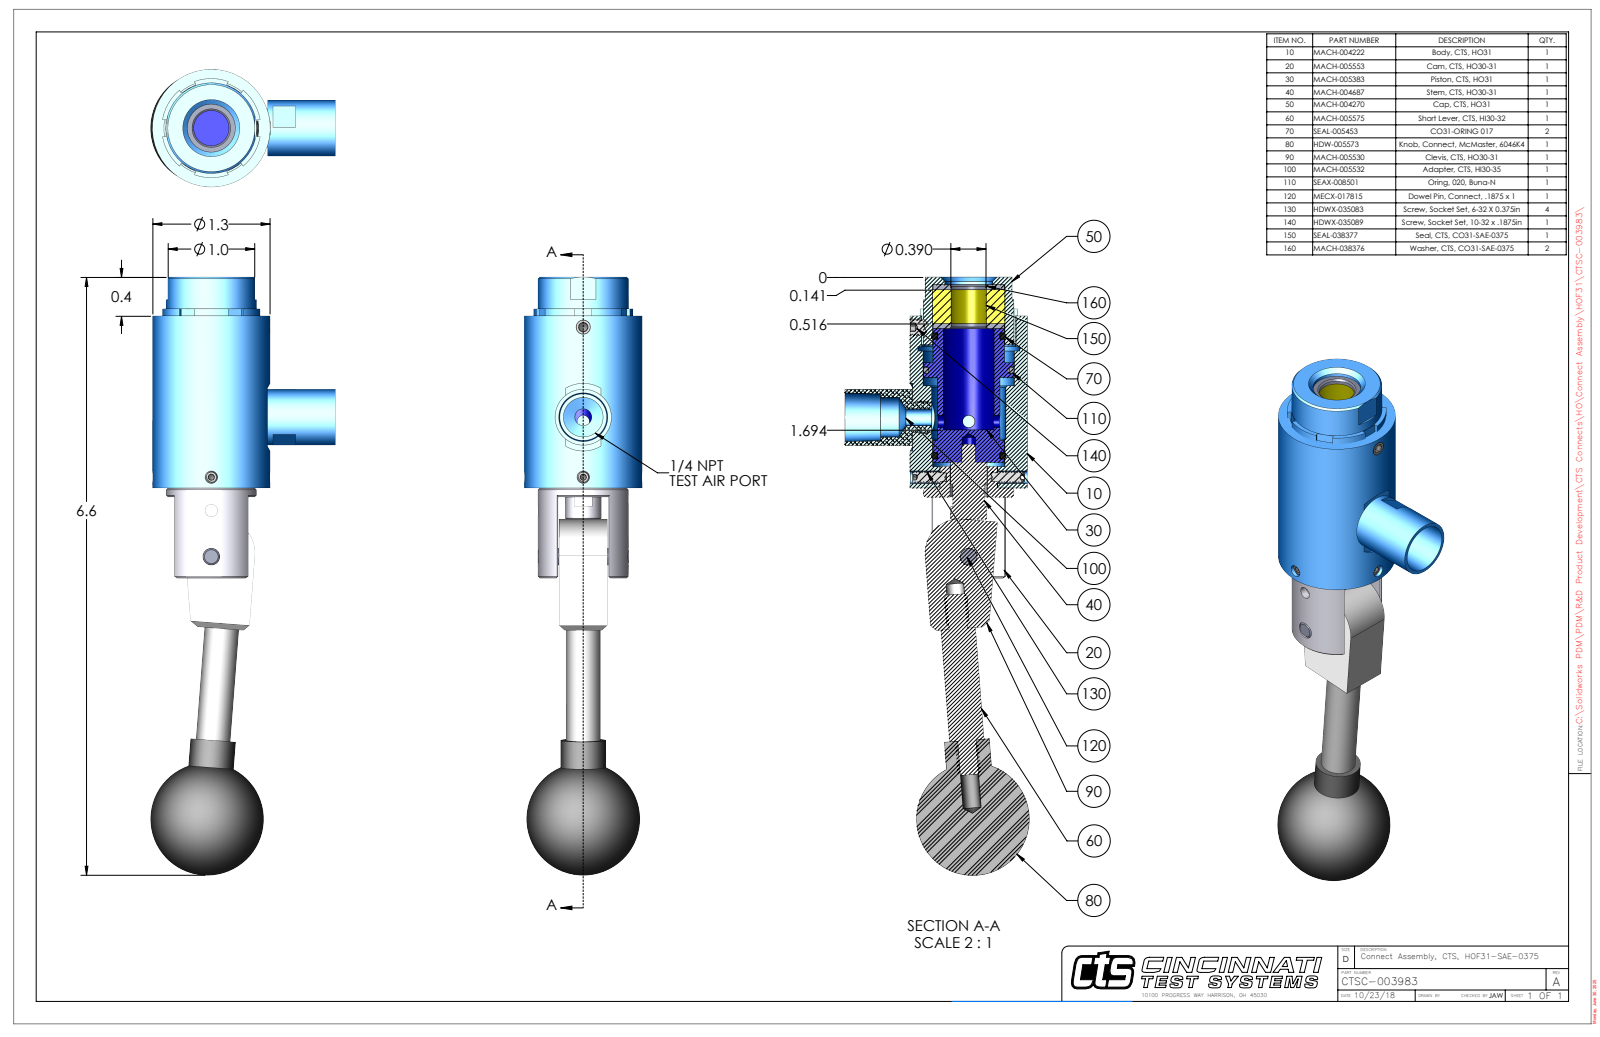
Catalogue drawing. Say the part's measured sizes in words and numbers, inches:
The part is named "CTSC-003983". Its 3-D file was written by "SolidWorks 2023 (AUTOMOTIVE_DESIGN)". It is 14 solids with 532 faces: 173 planar, 217 cylindrical and 142 other. Overall it measures 6.63 by 2.042 by 1.3 inches. Its volume is 4.511 cubic inches and its surface area 46.57 square inches. Round holes: 2 of diameter 0.136, 2 of diameter 0.201, 1 of diameter 0.138, 1 of diameter 0.15, 1 of diameter 0.159, 1 of diameter 0.187, 1 of diameter 0.189, 1 of diameter 0.19, 1 of diameter 0.332, 1 of diameter 0.39, 1 of diameter 0.418, 1 of diameter 0.438. Round bosses or shafts: 2 of diameter 0.138, 1 of diameter 1.3, 1 of diameter 1, 1 of diameter 0.79, 1 of diameter 0.69, 1 of diameter 0.63, 1 of diameter 0.62, 1 of diameter 0.5. Partial cylindrical surfaces (rounded edges, fillets, slot ends): 1 of radius 0.374, 1 of radius 0.375, 1 of radius 0.524, 1 of radius 0.547. The main face-to-face distances are 0.012, 0.542, 0.056, 0.431, 0.53, 0.375, 0.554, 1.822, 2.197, 2.253. The hole center spacings are 0.047, 0.51, 0.987, 0.997, 1.044, 1.497.
